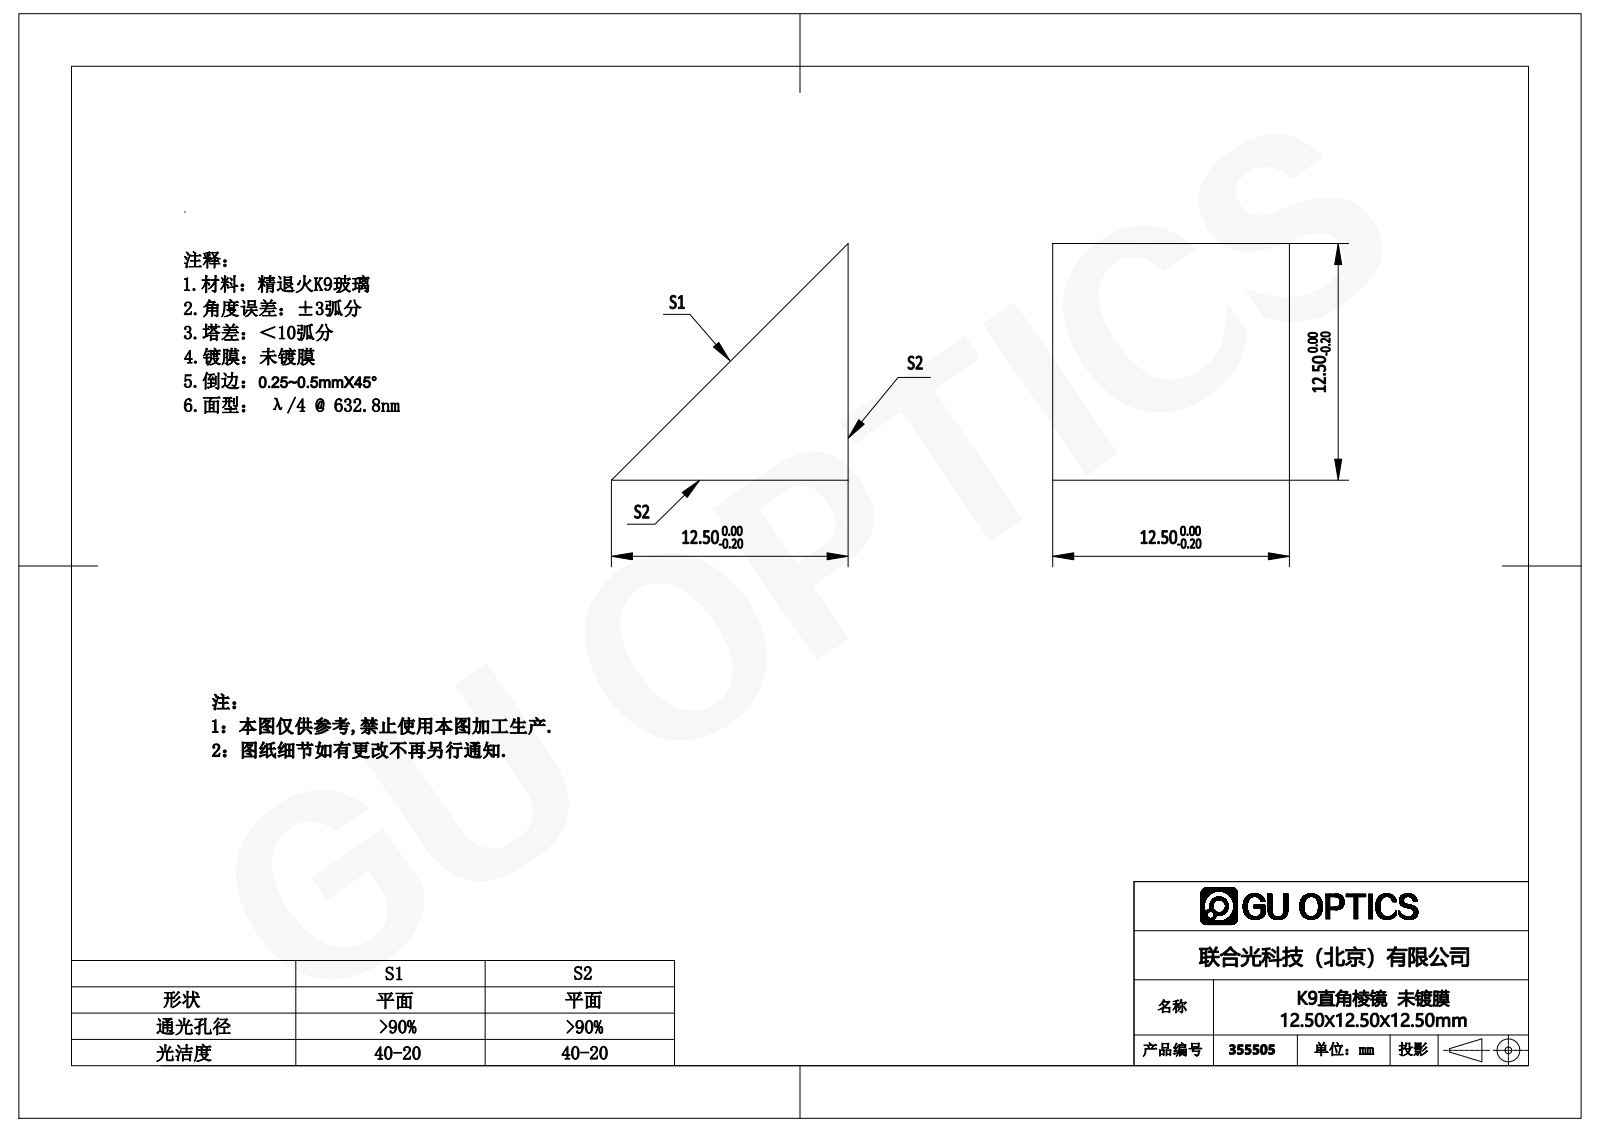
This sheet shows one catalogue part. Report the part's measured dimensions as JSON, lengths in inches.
{"part_name": "355505", "step_written_by": "SolidWorks 2016 (CONFIG_CONTROL_DESIGN)", "units": "inches", "bodies": {"solids": 1, "faces": 5, "planar": 5, "cylindrical": 0, "other": 0}, "overall_size": [0.492, 0.492, 0.492], "volume_in3": 0.06, "surface_area_in2": 1.07, "face_to_face_distances": [0.492]}
